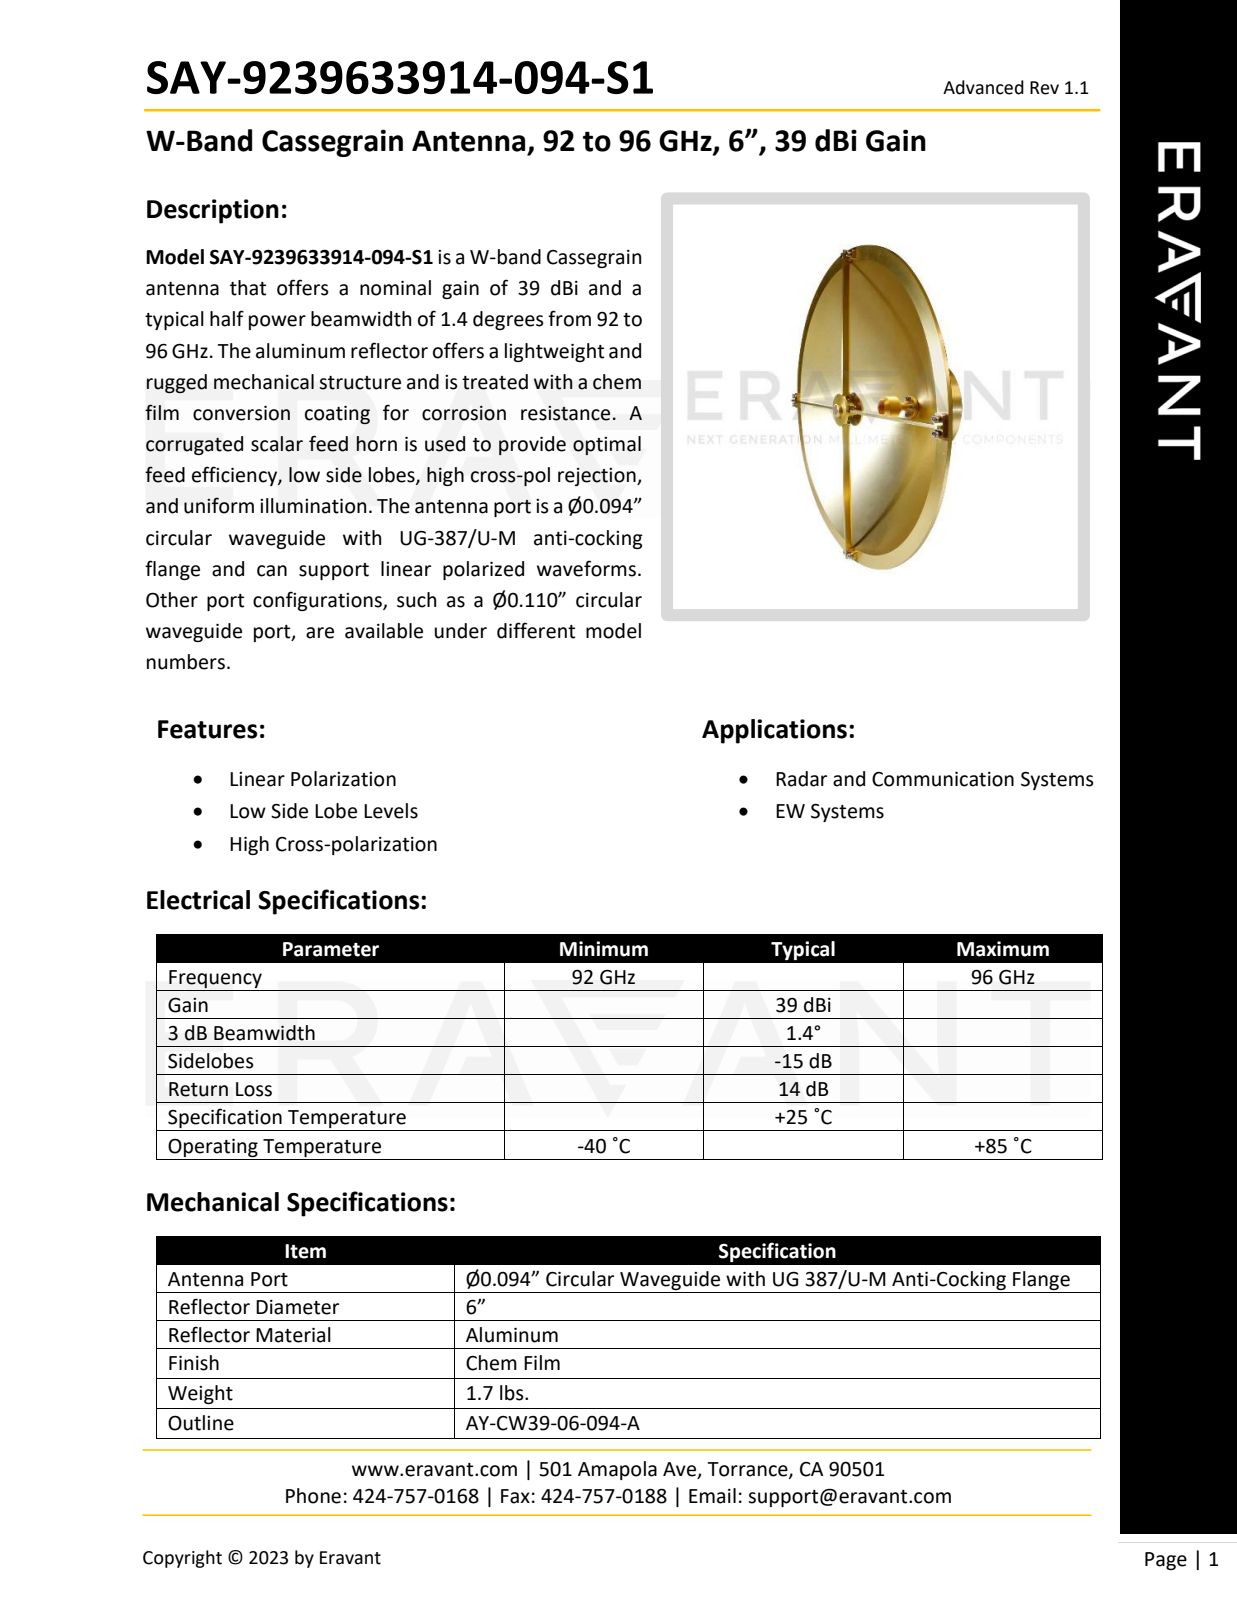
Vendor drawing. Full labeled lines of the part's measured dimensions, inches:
Part name (STEP PRODUCT): SAY-9239633914-094-S1
STEP written by: SolidWorks 2021 (CONFIG_CONTROL_DESIGN)
Units: inches
Bodies: 45 solids, 1138 faces (437 planar, 317 cylindrical, 384 other)
Overall size (bounding box): 6.85 × 6.85 × 3.49
Volume: 16.16 in³ · Surface area: 128 in²
Round holes (diameter × count): ⌀0.12 ×21, ⌀0.089 ×20, ⌀0.07 ×8, ⌀0.136 ×8, ⌀0.14 ×4, ⌀0.188 ×4, ⌀0.061 ×2, ⌀0.067 ×2, ⌀0.063 ×1, ⌀0.094 ×1, ⌀0.225 ×1, ⌀0.68 ×1
Round bosses / shafts (diameter × count): ⌀0.183 ×16, ⌀0.112 ×16, ⌀0.18 ×12, ⌀0.086 ×8, ⌀0.063 ×2, ⌀6.85 ×1, ⌀3.15 ×1, ⌀1.325 ×1
Partial cylindrical surfaces — rounded edges, fillets, slot ends (radius × count): R0.06 ×24, R0.01 ×8, R0.04 ×8, R0.18 ×1
Main face-to-face distances: 0.184, 2.629, 2.813, 0.079, 0.085, 0.073, 3.072, 0.444, 0.26, 2.922
Hole centre spacings: 3.476, 3.75, 2.641, 4.519, 4.519, 6.382, 0.215, 0.281
